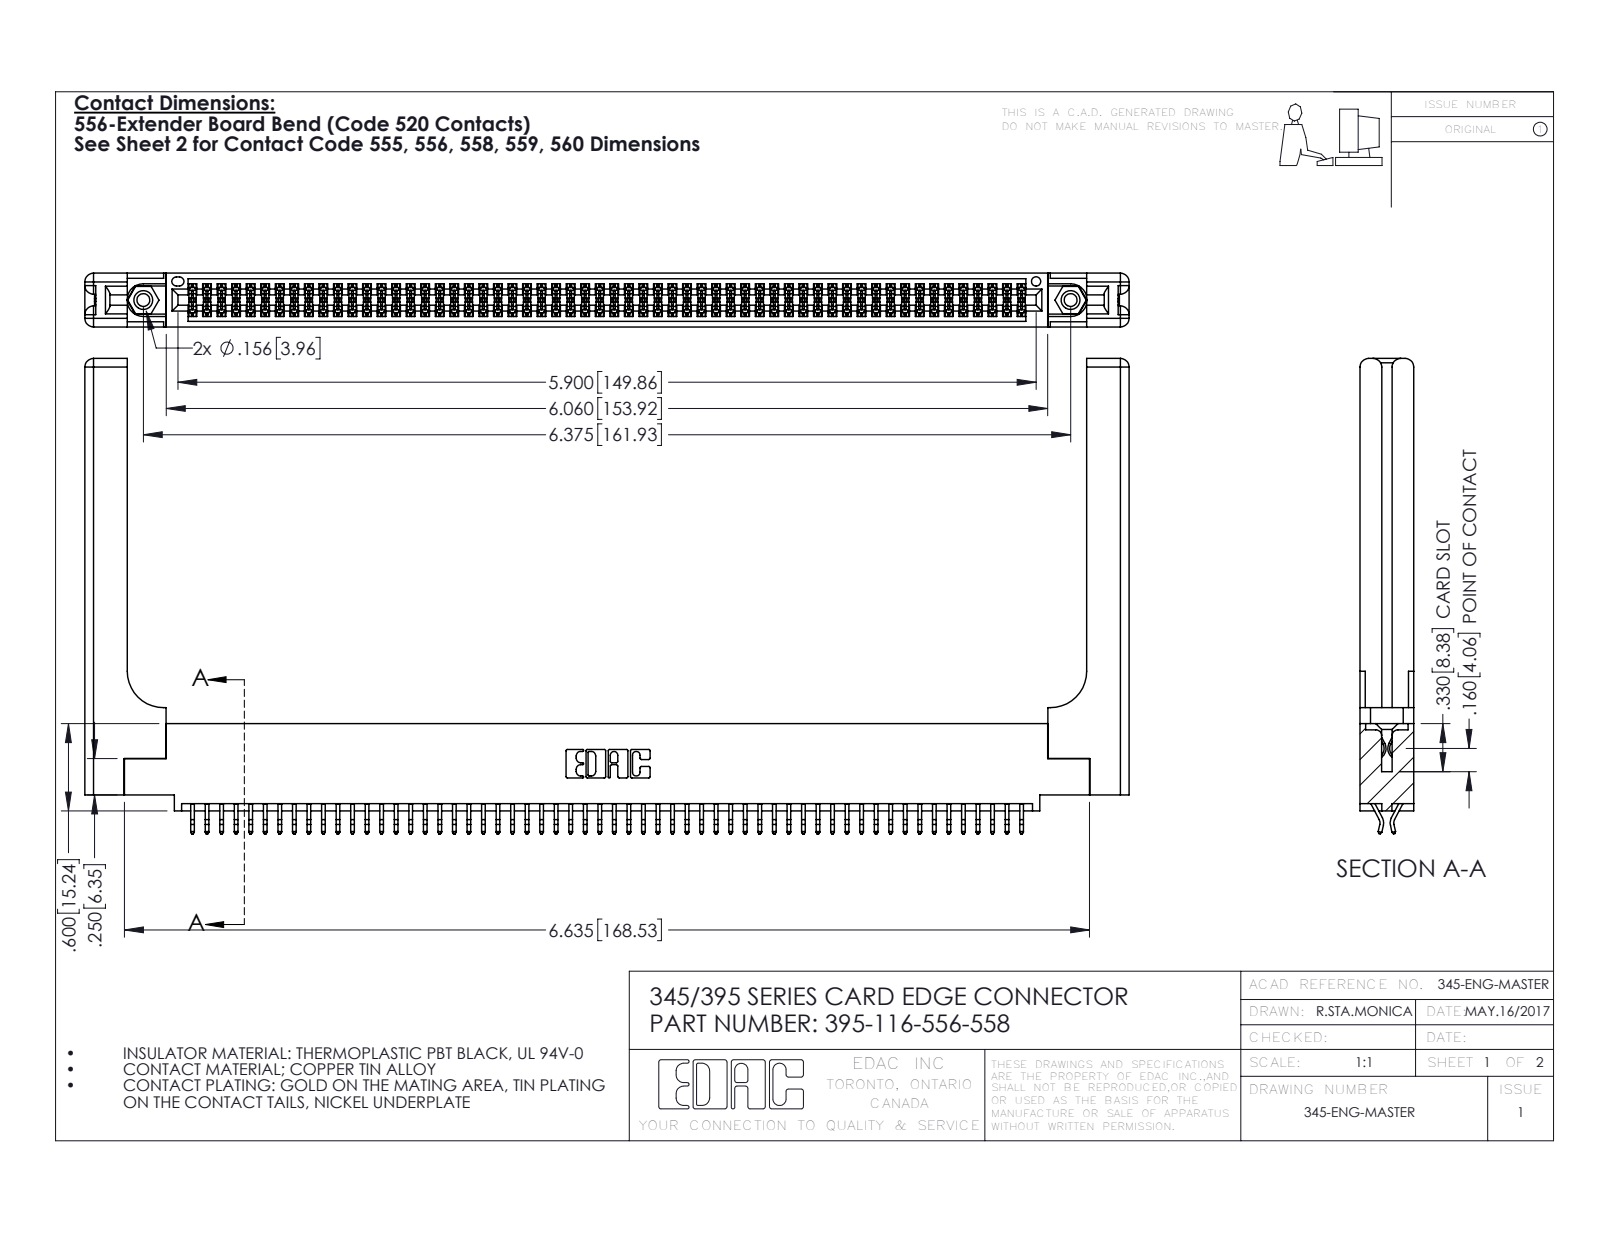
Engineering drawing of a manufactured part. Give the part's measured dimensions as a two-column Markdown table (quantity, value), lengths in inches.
| quantity | value |
| --- | --- |
| part name | 345 Part_0.110 Offset - 0.156 Dia-TH; 345-250-001_345-250-001-102; 395-116-556-558; 345-220-058_345-220-058 (+1 more) |
| STEP written by | SolidWorks 2016 (CONFIG_CONTROL_DESIGN) |
| units | inches |
| bodies | 121 solids, 6882 faces (4524 planar, 2298 cylindrical, 60 other) |
| overall size | 7.179 × 3.267 × 0.37 |
| volume | 1.602 in³ |
| surface area | 49.05 in² |
| round holes (diameter × count) | 0.089 × 2, 0.125 × 2, 0.156 × 2, 0.064 × 1 |
| round bosses / shafts (diameter × count) | 0.155 × 2 |
| partial cylindrical surfaces (radius × count) | 0.006 × 174, 0.01 × 22, 0.06 × 16, 0.007 × 6, 0.031 × 6, 0.026 × 3, 0.01 × 2, 0.014 × 2 |
| main face-to-face distances | 0.072, 0.298, 0.37, 0.025, 0.098, 0.272, 0.2, 0.225, 0.148, 0.15 |
| hole center spacings | 0.27, 6.139, 6.375 |
